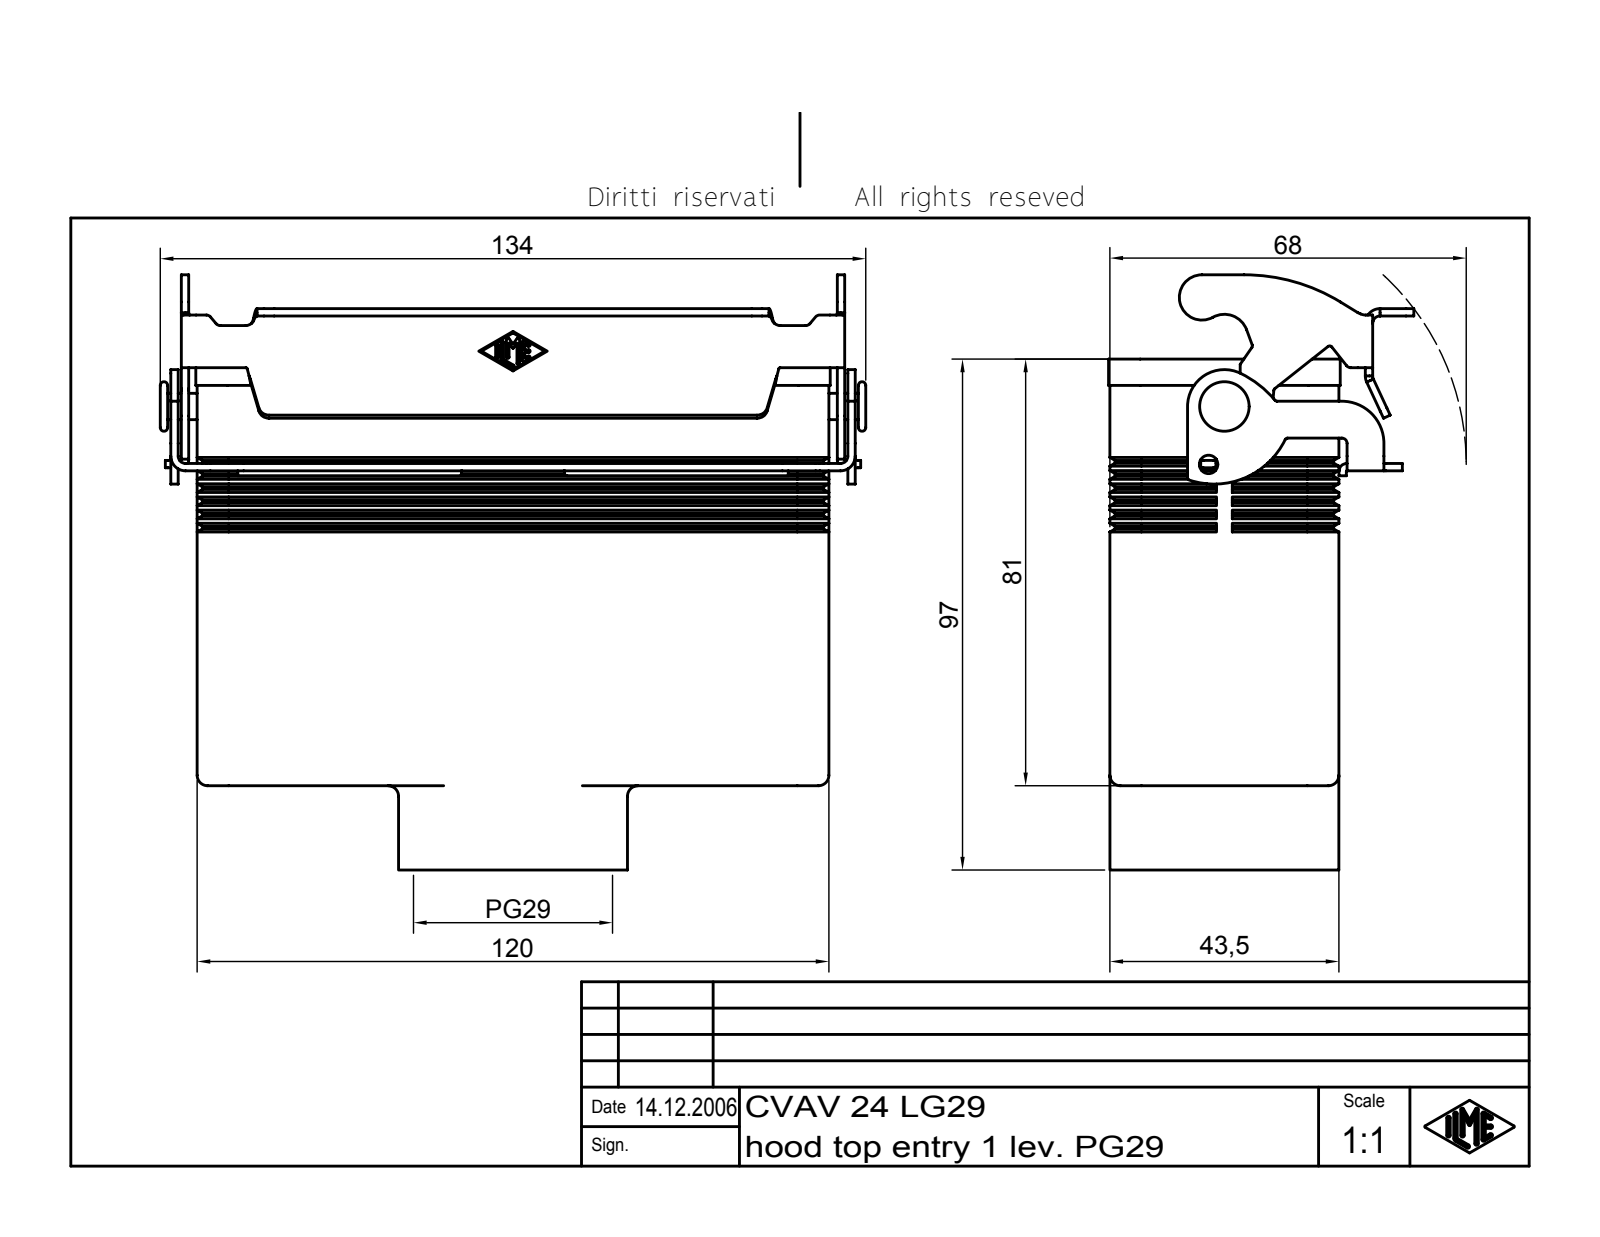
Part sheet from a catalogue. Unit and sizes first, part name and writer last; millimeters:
Units: millimetres
Overall size (bounding box): 134 × 113 × 57.98
Round holes (diameter × count): ⌀3.5 ×1, ⌀32.48 ×1, ⌀35.48 ×1
Round bosses / shafts (diameter × count): ⌀43.48 ×1, ⌀5 ×1, ⌀3.2 ×1
Partial cylindrical surfaces — rounded edges, fillets, slot ends (radius × count): R0.25 ×15, R2 ×10, R0.5 ×9, R1.5 ×9, R1 ×8, R6 ×8, R1.4 ×6, R2.8 ×6
Main face-to-face distances: 3, 40.5, 37.5, 43.5, 117, 120, 1.4, 11.75, 8.75, 11.5
Volume: 120 414 mm³ · Surface area: 79 700 mm²
Bodies: 2 solids, 621 faces (195 planar, 147 cylindrical, 279 other)
Part name (STEP PRODUCT): CVAV 24 LG29
STEP written by: Autodesk Inventor 7 (AUTOMOTIVE_DESIGN)
